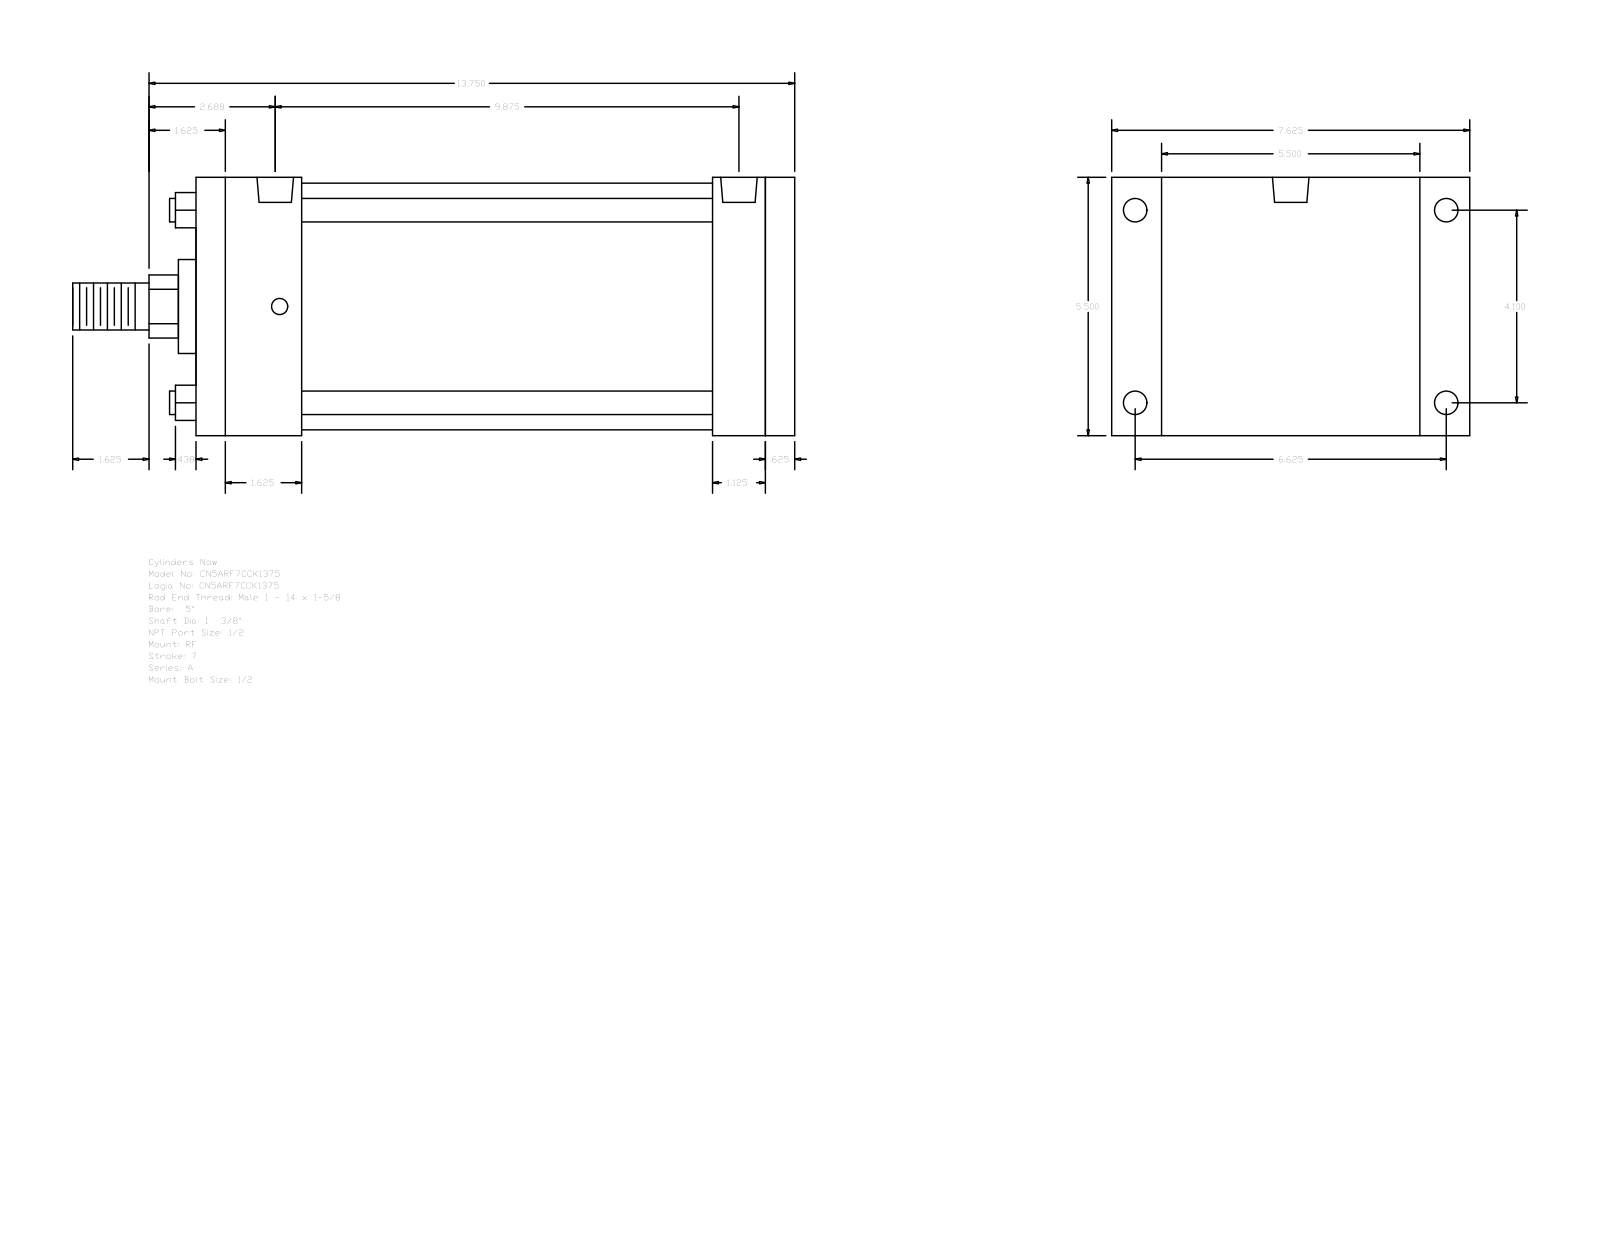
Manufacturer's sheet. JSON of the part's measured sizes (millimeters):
{"part_name": "A_RF__0500_1.375", "step_written_by": "GSSL Pune (CONFIG_CONTROL_DESIGN)", "units": "millimeters", "bodies": {"solids": 0, "faces": 92, "planar": 64, "cylindrical": 28, "other": 0}, "overall_size": [390.52, 193.68, 139.7], "round_holes": [[8.73, 4], [12.7, 4], [19.77, 2]], "round_bosses_or_shafts": [[12.7, 4], [133.35, 1], [50.8, 1], [34.92, 1], [25.4, 1]], "partial_cylinders_radius": [[17.06, 1]], "face_to_face_distances": [139.7, 323.85, 307.98, 15.87, 57.15, 28.58, 250.83, 266.7, 279.4, 222.25], "hole_center_spacings": [2.39, 104.14, 168.28, 197.9, 246.05, 248.44, 250.83]}
